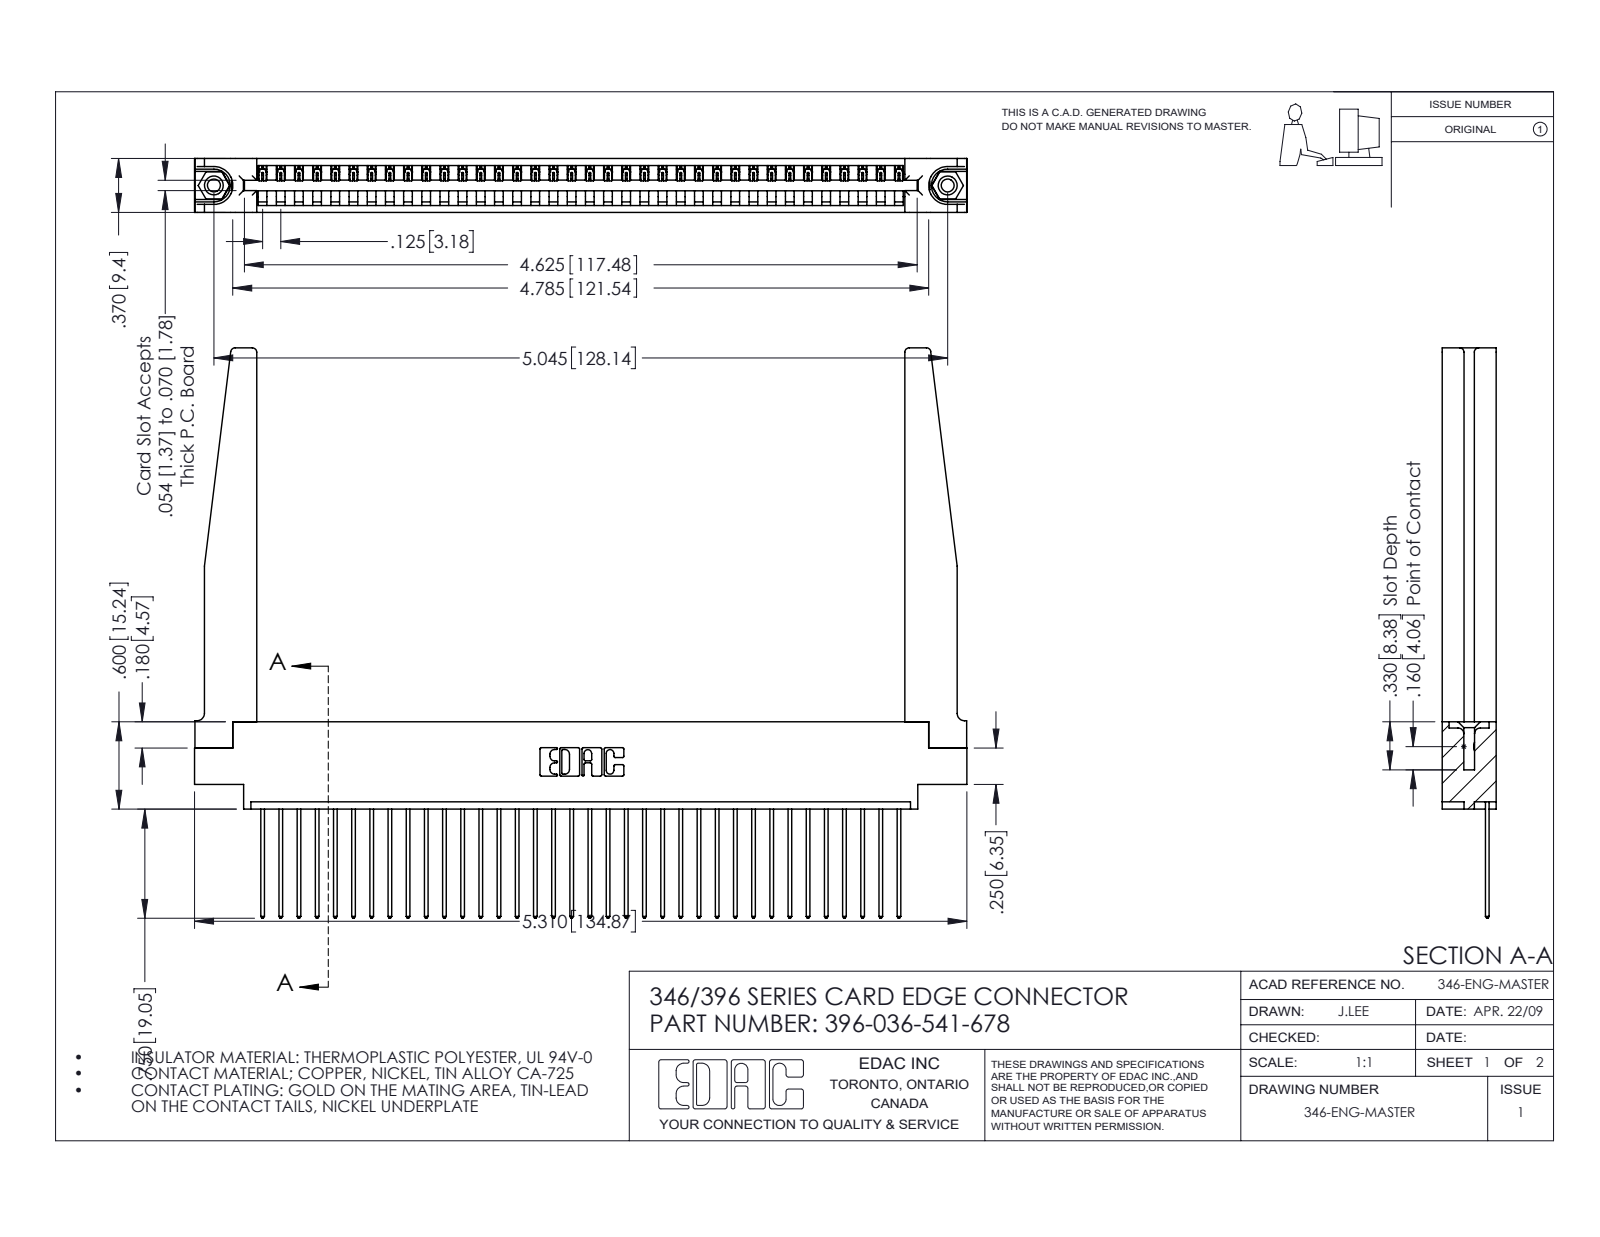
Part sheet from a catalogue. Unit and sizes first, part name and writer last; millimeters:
Units: millimetres
Overall size (bounding box): 134.9 × 99.6 × 9.4
Round holes (diameter × count): ⌀2.3 ×2, ⌀3.2 ×2, ⌀4 ×2, ⌀1.6 ×1
Round bosses / shafts (diameter × count): ⌀3.9 ×2
Partial cylindrical surfaces — rounded edges, fillets, slot ends (radius × count): R0.2 ×72, R0.3 ×72, R0.3 ×22, R0.8 ×8, R0.2 ×6, R0.8 ×6, R0.7 ×3, R0.8 ×2
Main face-to-face distances: 9.4, 1.2, 8.2, 1.8, 3.8, 3.8, 6.4, 7.6, 0.6, 5.6
Hole centre spacings: 6.2, 122.8, 128.1
Volume: 19 750 mm³ · Surface area: 23 390 mm²
Bodies: 41 solids, 2448 faces (1662 planar, 734 cylindrical, 52 other)
Part name (STEP PRODUCT): 346 Part_0.170 Offset - 0.156 Dia-TH; 345-250-001_345-250-001-102; 346-220-078_345-220-078; 345-292-001_345-293-141 (+1 more)
STEP written by: SolidWorks 2016 (CONFIG_CONTROL_DESIGN)
